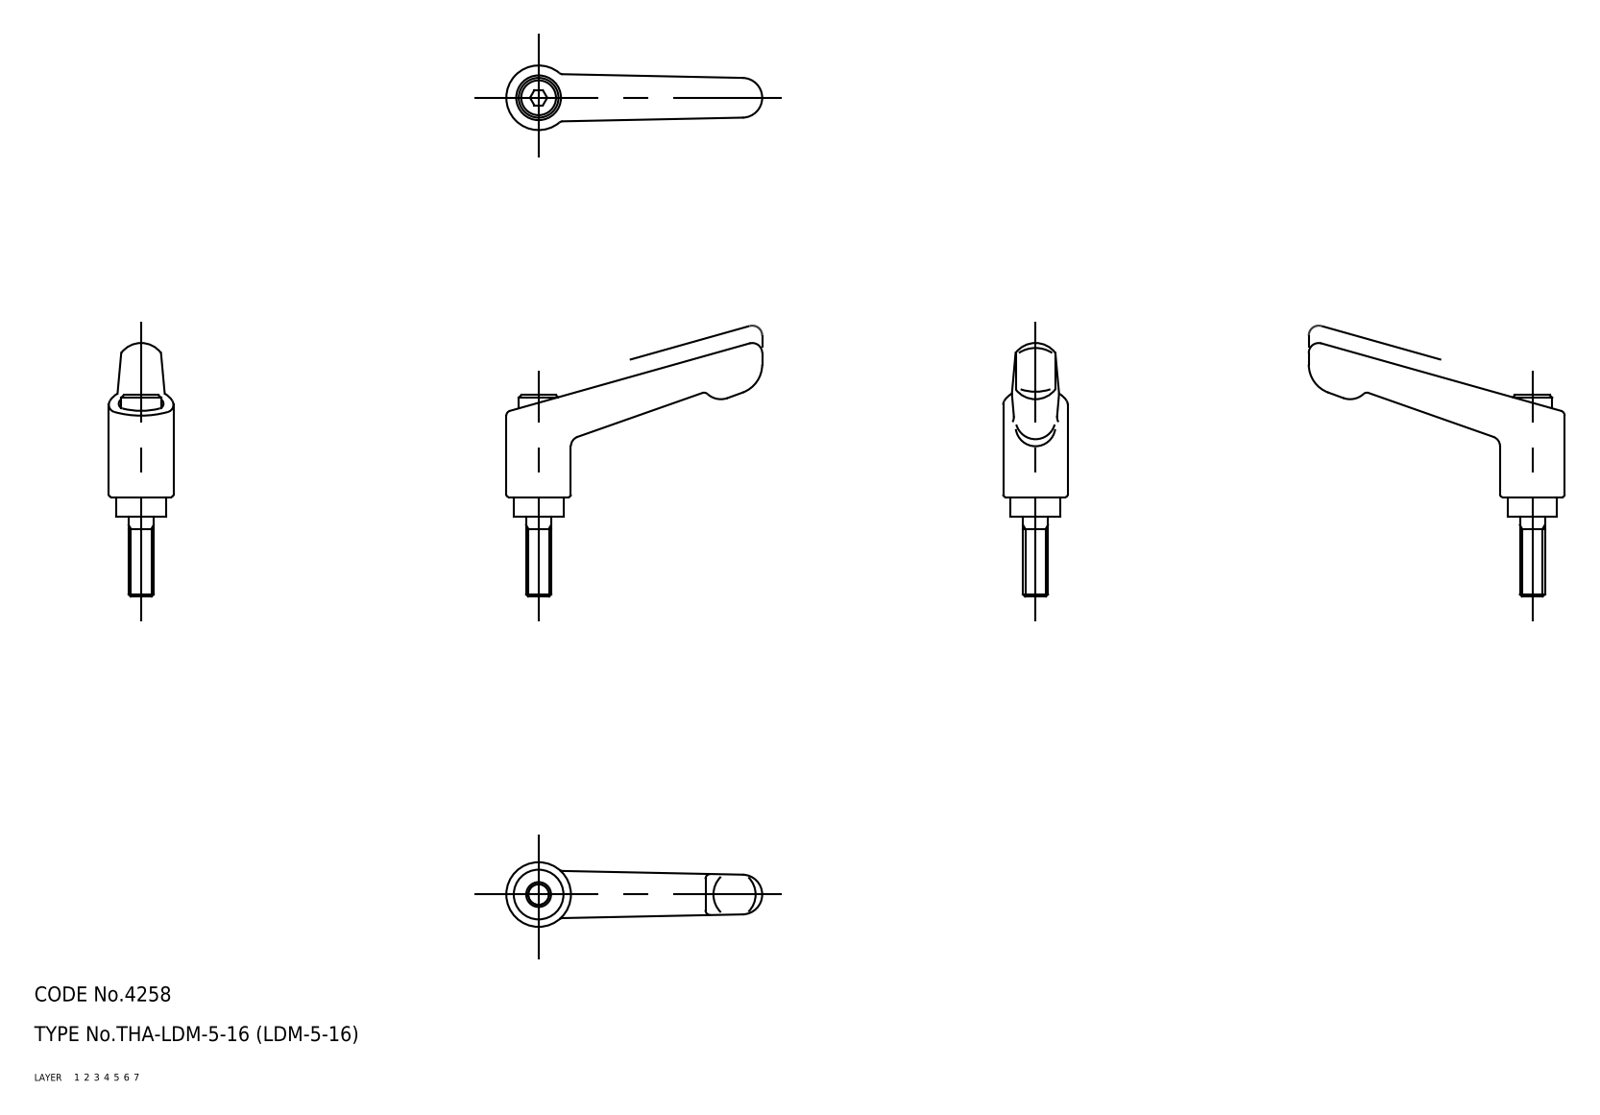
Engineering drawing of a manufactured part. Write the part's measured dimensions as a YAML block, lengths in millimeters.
part_name: "sleeve; screw; handle; LDM_5_16_12715_36"
step_written_by: "CADfix (AUTOMOTIVE_DESIGN)"
units: millimeters
bodies: {solids: 3, faces: 70, planar: 0, cylindrical: 0, other: 70}
overall_size: [51.5, 51, 13]
volume: 5444
surface_area: 3768
